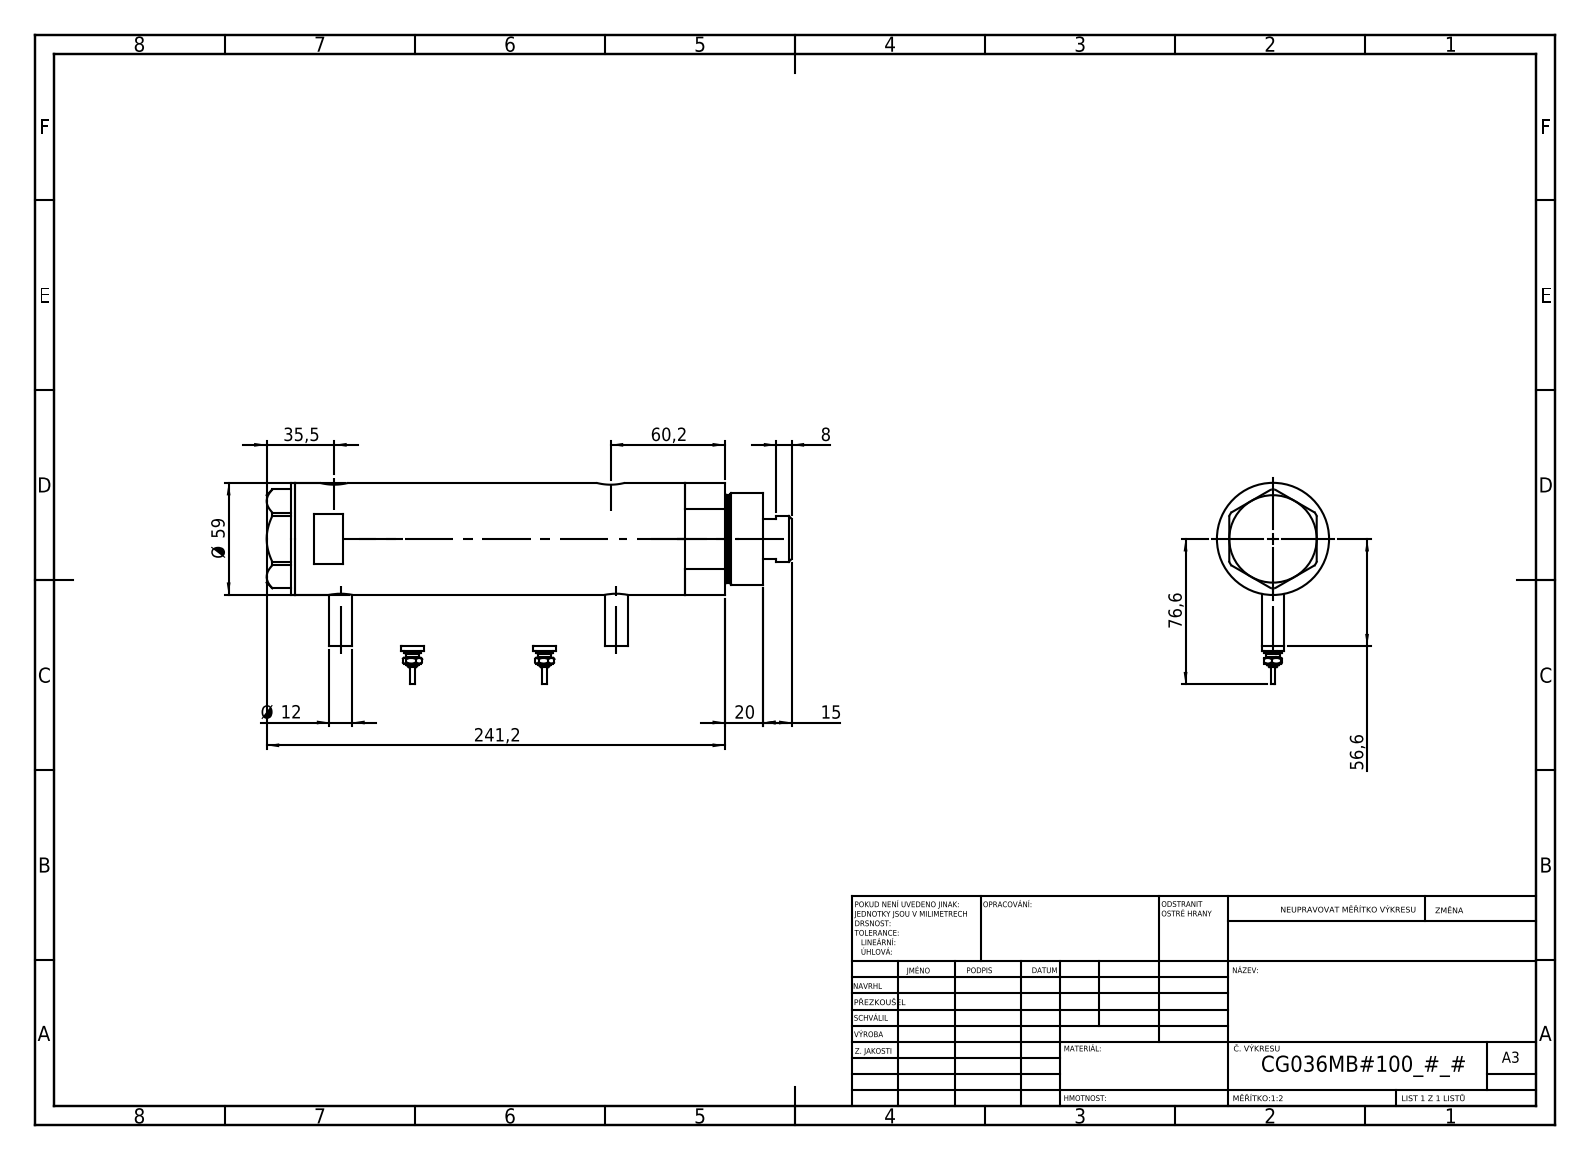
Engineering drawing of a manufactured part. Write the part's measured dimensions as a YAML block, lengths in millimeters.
part_name: "V270CG_BACK; V270CG_FRONT; V270CG_MIDDLE; V270CG_VC (+1 more)"
step_written_by: "SolidWorks 2019 (CONFIG_CONTROL_DESIGN)"
units: millimeters
bodies: {solids: 6, faces: 212, planar: 79, cylindrical: 69, other: 64}
overall_size: [276.2, 106.1, 59]
volume: 635816
surface_area: 127776
round_holes:
  - {diameter: 9.73, count: 2}
  - {diameter: 12.5, count: 2}
  - {diameter: 15, count: 2}
  - {diameter: 8.5, count: 1}
  - {diameter: 25, count: 1}
  - {diameter: 26.5, count: 1}
  - {diameter: 36, count: 1}
  - {diameter: 40, count: 1}
  - {diameter: 52, count: 1}
round_bosses_or_shafts:
  - {diameter: 12, count: 4}
  - {diameter: 9, count: 2}
  - {diameter: 7, count: 2}
  - {diameter: 4.5, count: 2}
  - {diameter: 2.5, count: 2}
  - {diameter: 59, count: 1}
  - {diameter: 48, count: 1}
  - {diameter: 46, count: 1}
face_to_face_distances: [167.2, 23.5, 143.7, 15, 38.5, 182.2, 2, 261.2, 246.2, 222.7]
hole_center_spacings: [2.9, 3.5, 142, 144.9, 145.5, 148.4]
